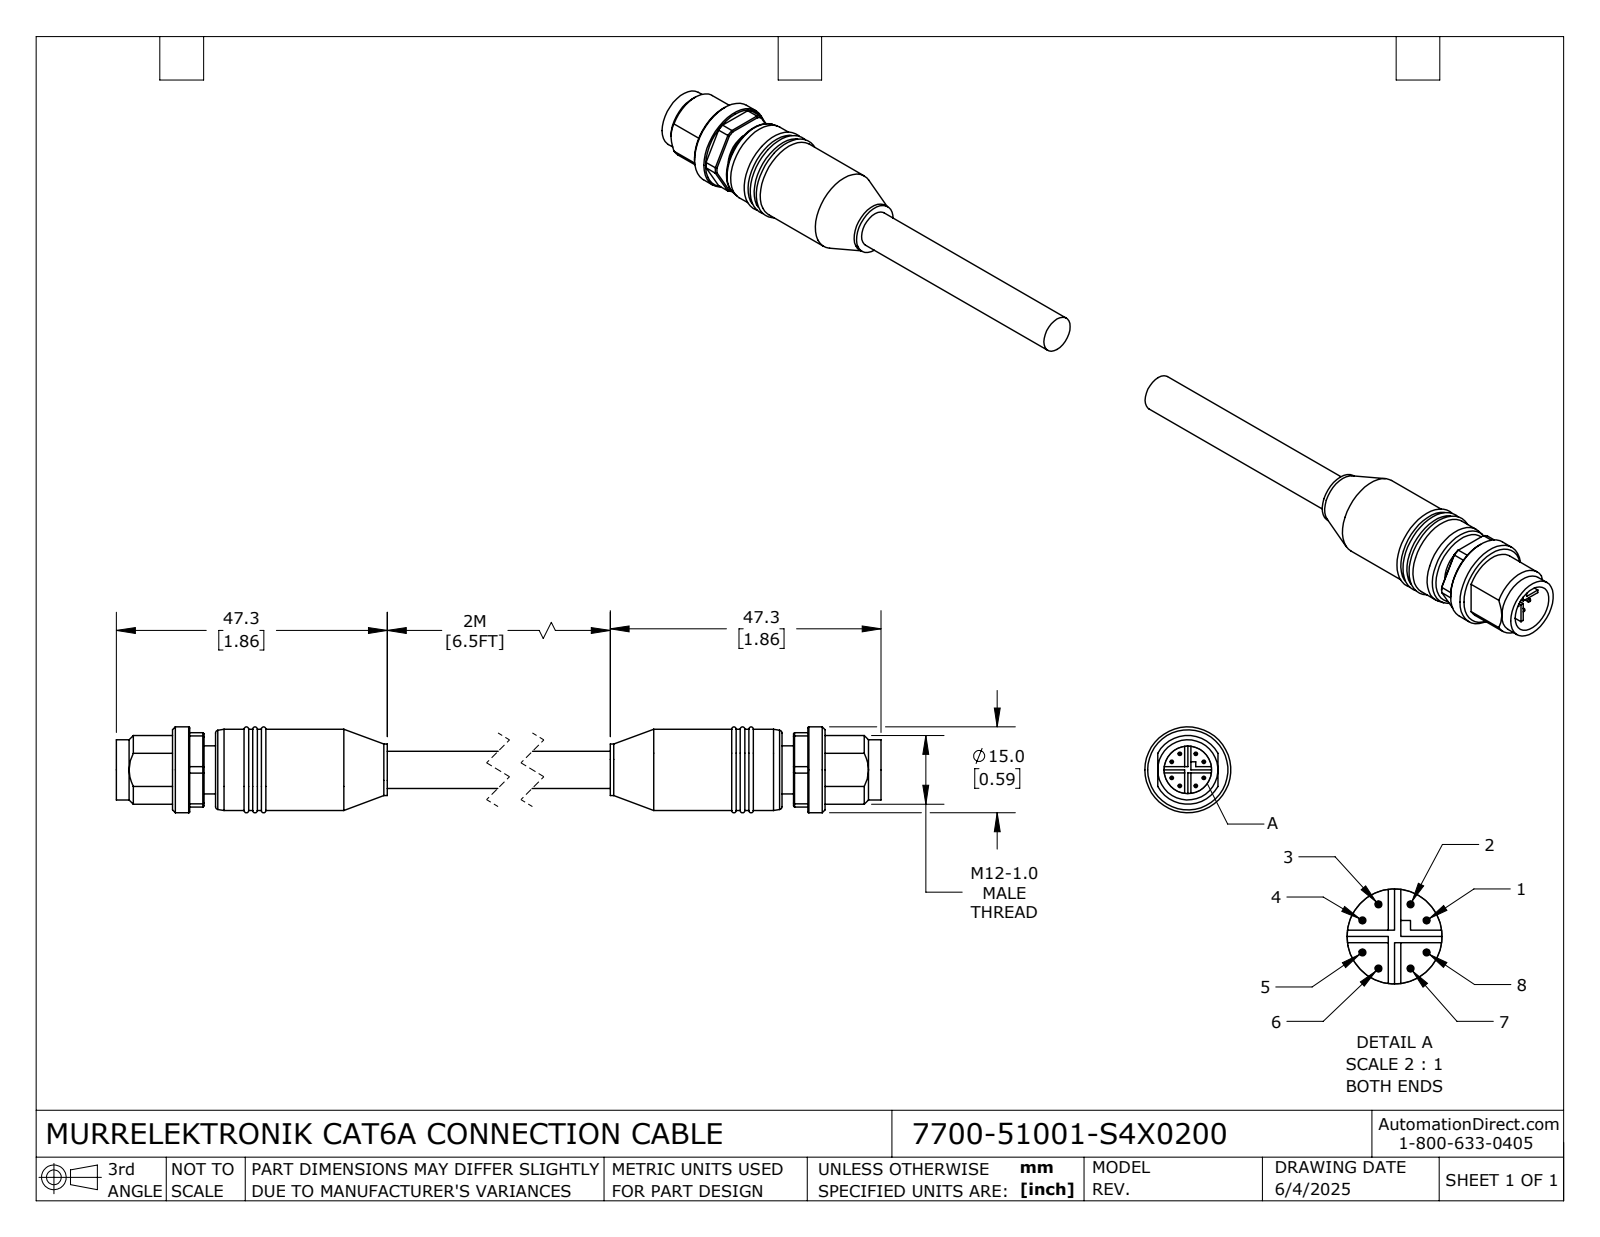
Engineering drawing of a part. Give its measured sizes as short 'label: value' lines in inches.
name: 7700-51001-S4X0200_MALE; 7700-51001-S4X0200
written by: SolidWorks 2024 (CONFIG_CONTROL_DESIGN)
unit: in
bodies: 2 solids, 282 faces (112 planar, 88 cylindrical, 82 other)
size: 8.252 × 0.591 × 0.591
volume: 0.912 in³; area: 11.83 in²
holes: 1× ⌀0.327
bosses: 8× ⌀0.024, 1× ⌀0.591, 1× ⌀0.559, 1× ⌀0.413, 1× ⌀0.354, 1× ⌀0.331, 1× ⌀0.256
rounds: 1× R0.236, 1× R0.283
face distances: 0.185, 0.228, 0.079, 6.969, 0.043, 0.217, 0.512, 0.295, 7.185, 7.264
